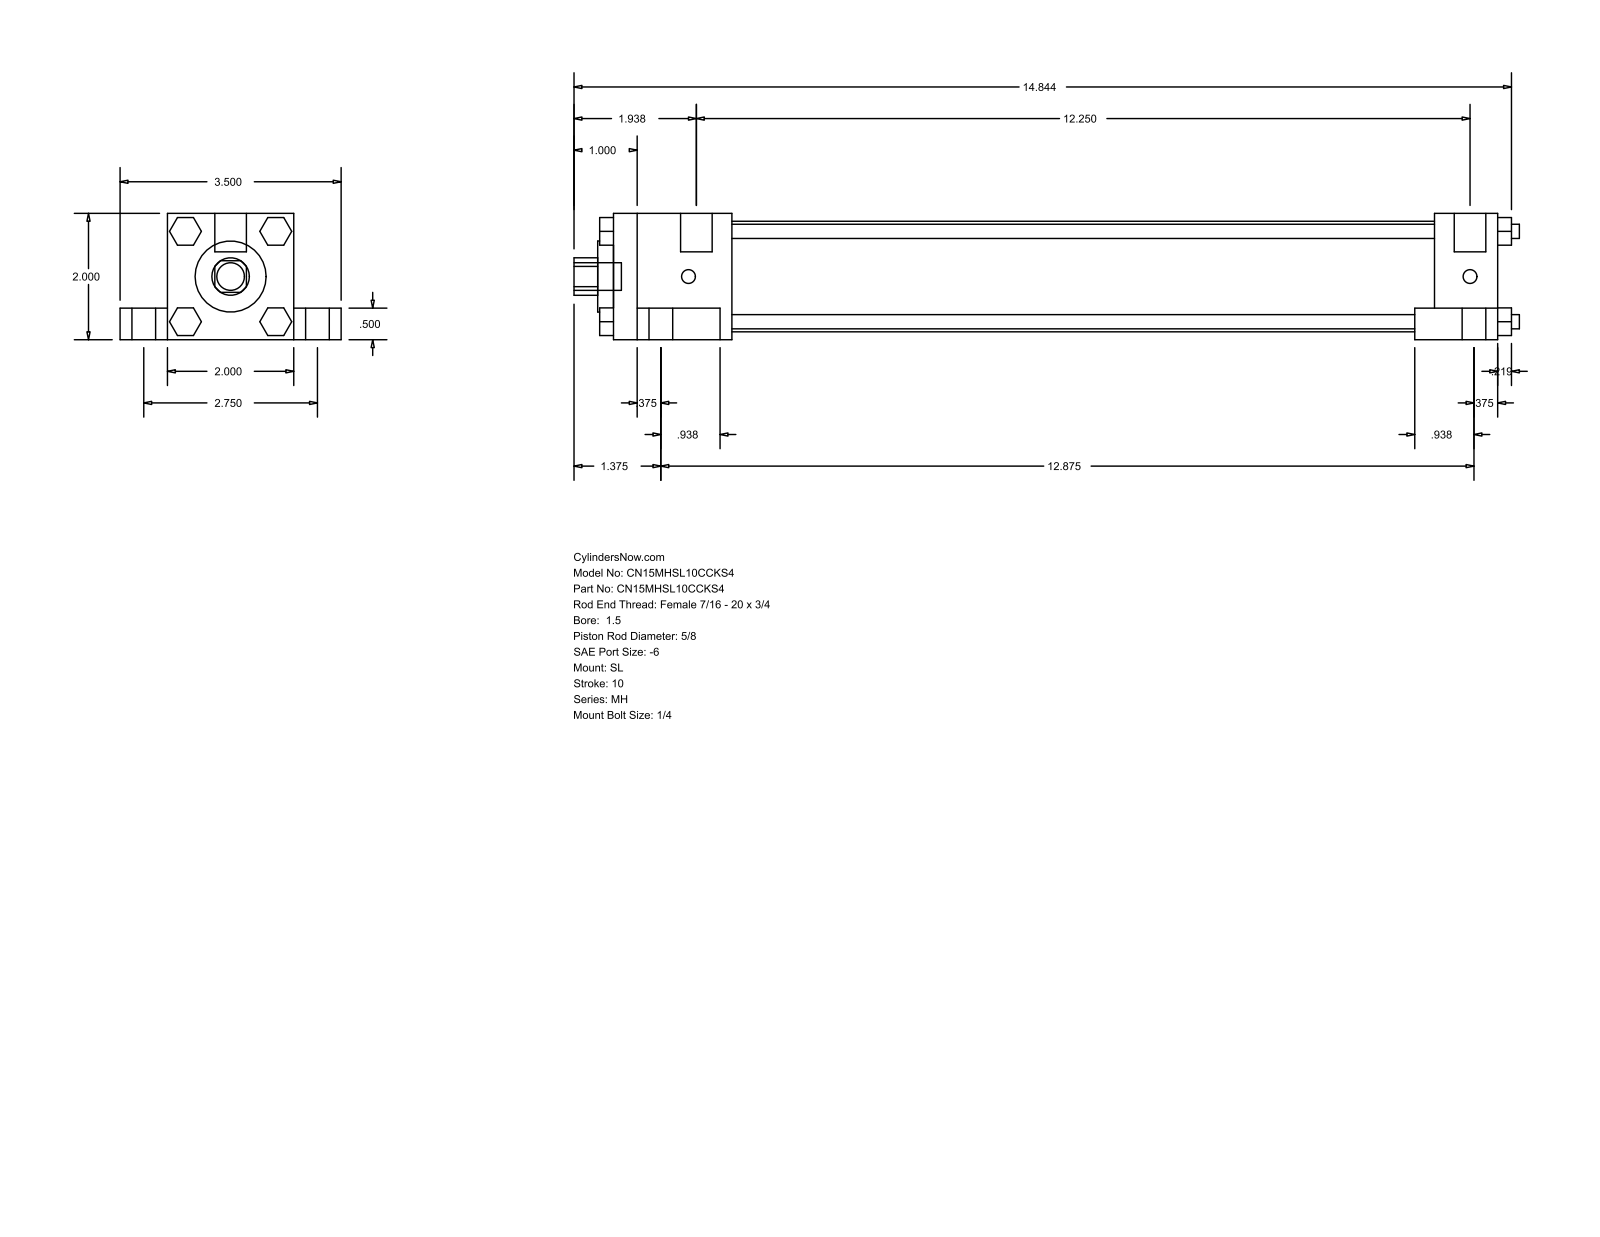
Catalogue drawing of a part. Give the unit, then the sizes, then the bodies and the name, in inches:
Units: inches
Overall size (bounding box): 14.969 × 3.5 × 2
Round holes (diameter × count): ⌀0.625 ×1, ⌀1.125 ×1, ⌀1.75 ×1
Round bosses / shafts (diameter × count): ⌀0.625 ×4, ⌀0.375 ×4, ⌀0.225 ×4, ⌀0.219 ×4, ⌀0.5 ×2, ⌀0.437 ×1
Partial cylindrical surfaces — rounded edges, fillets, slot ends (radius × count): R0.297 ×1
Main face-to-face distances: 2, 1.5, 0.75, 0.5, 2.75, 14, 0.375, 1.313, 12.313, 13
Bodies: 0 solids, 148 faces (112 planar, 36 cylindrical, 0 other)
Part name (STEP PRODUCT): MH_SL__0150_0.625
STEP written by: GSSL Pune (CONFIG_CONTROL_DESIGN)
